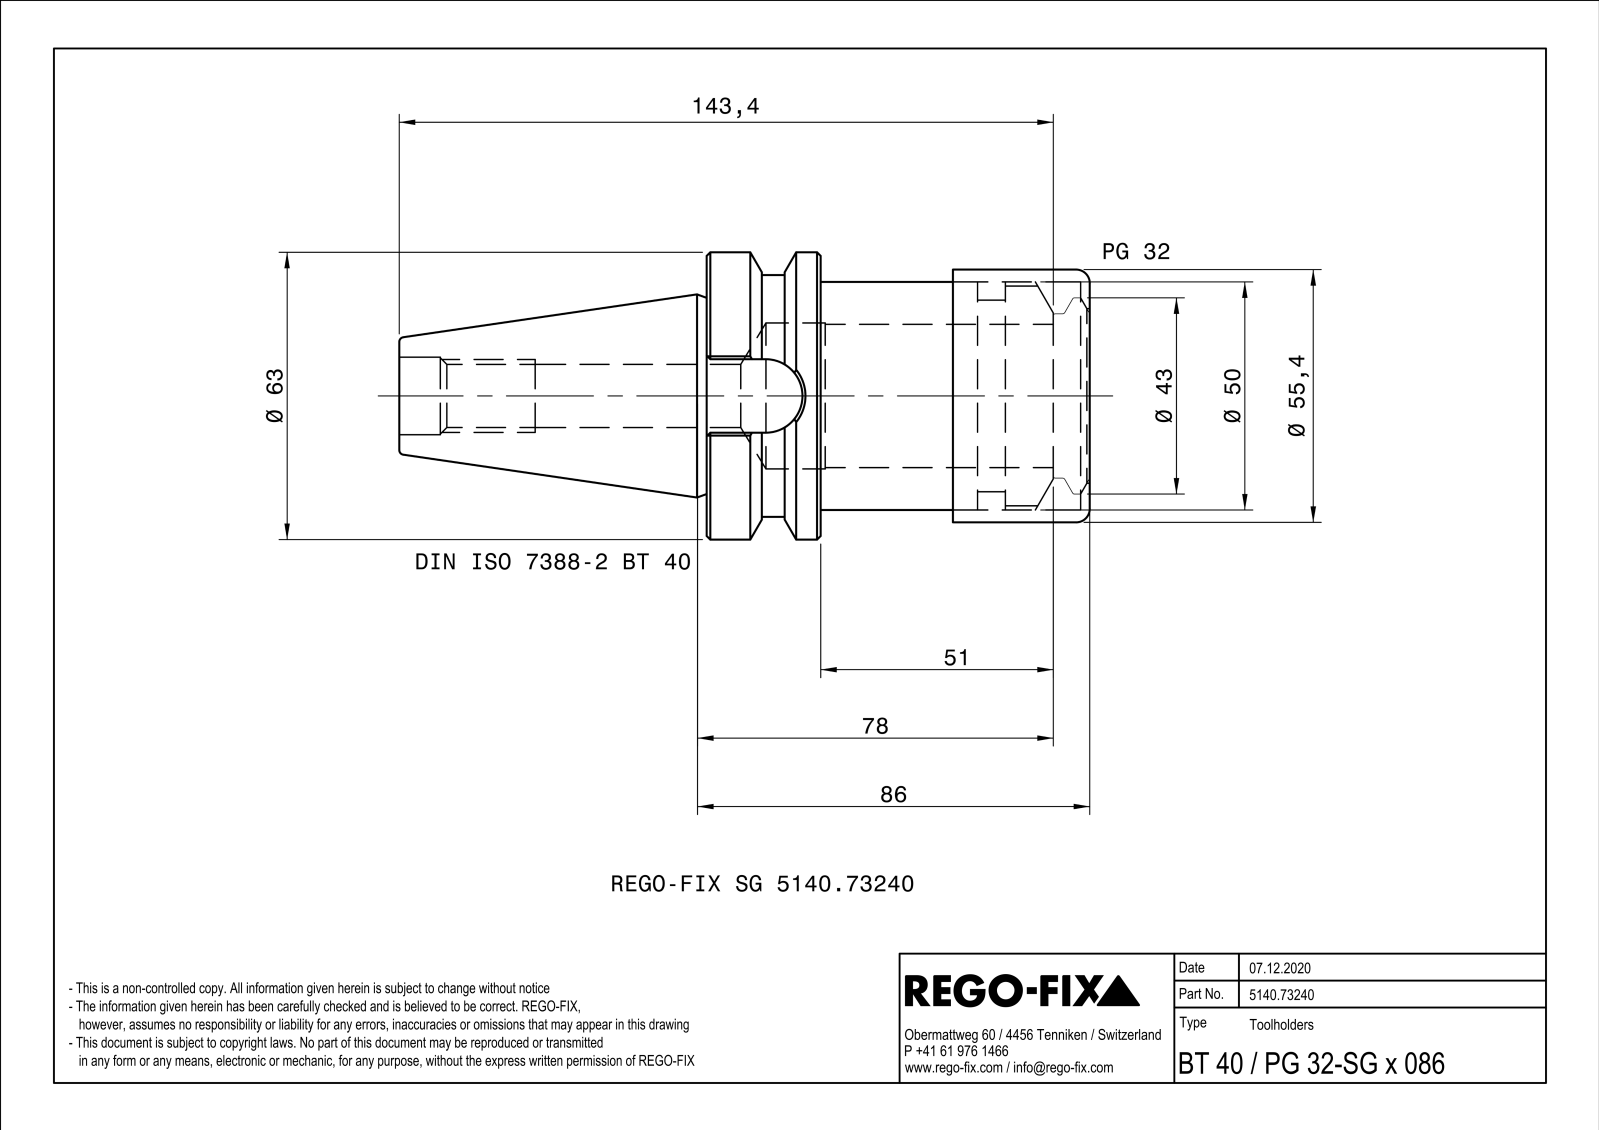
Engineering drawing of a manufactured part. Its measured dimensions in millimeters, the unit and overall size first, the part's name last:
Units: millimetres
Overall size (bounding box): 151.4 × 63 × 63
Round holes (diameter × count): ⌀13.84 ×1, ⌀17 ×1, ⌀33 ×1, ⌀38.25 ×1, ⌀48.38 ×1, ⌀50.05 ×1, ⌀51 ×1
Round bosses / shafts (diameter × count): ⌀63 ×1, ⌀55.4 ×1, ⌀55 ×1, ⌀53 ×1, ⌀50 ×1, ⌀42 ×1
Partial cylindrical surfaces — rounded edges, fillets, slot ends (radius × count): R0.5 ×4, R8.05 ×1
Main face-to-face distances: 84, 59, 25, 24.6, 34.4, 59.4, 18.5, 6.1, 40.5, 65.5
Volume: 177 760 mm³ · Surface area: 46 023 mm²
Bodies: 1 solid, 102 faces (42 planar, 22 cylindrical, 38 other)
Part name (STEP PRODUCT): NOCUT
STEP written by: SIEMENS PLM Software Solid Edge ST10 (AUTOMOTIVE_DESIGN)
